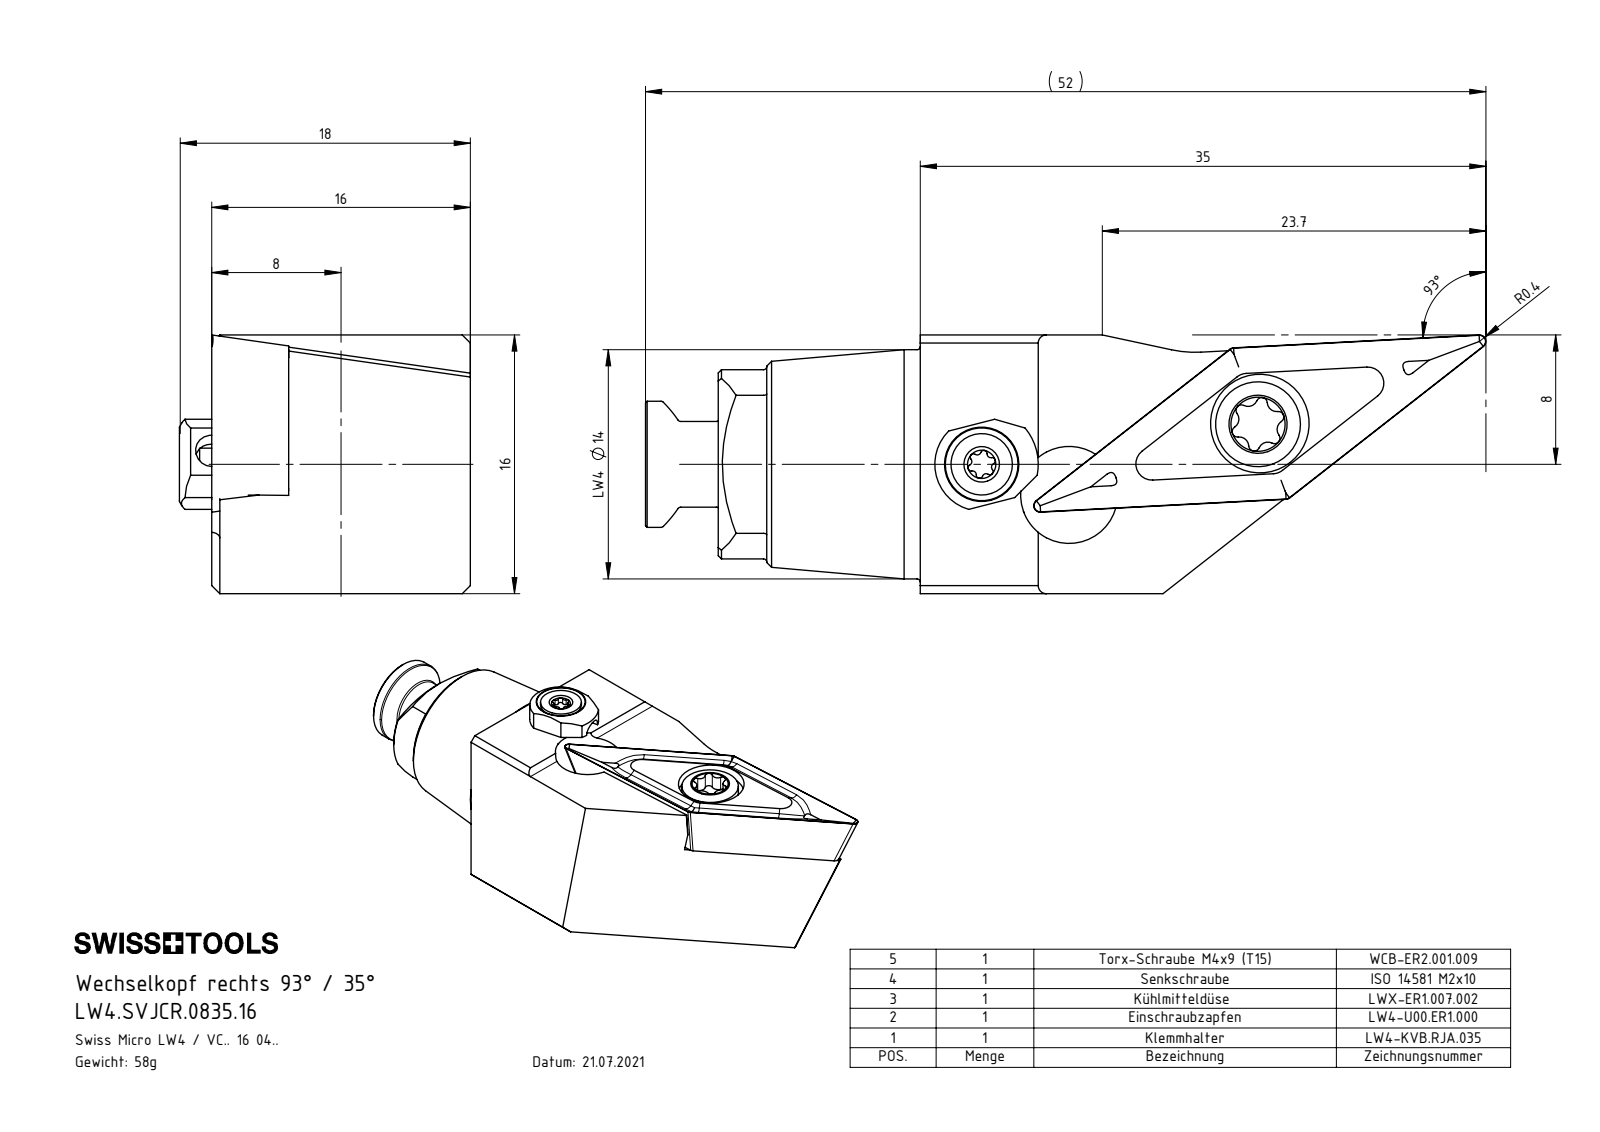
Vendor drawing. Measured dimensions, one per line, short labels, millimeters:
name: ISO 14581 - M2x10; LW4-U00.ER1.000_B; LW4-KVB.RJA.035_A; LWX-ER1.007.002 (+3 more)
written by: SolidWorks 2022 (CONFIG_CONTROL_DESIGN)
unit: mm
bodies: 6 solids, 270 faces (70 planar, 83 cylindrical, 117 other)
size: 52 × 18 × 16
volume: 6 929 mm³; area: 4 302 mm²
holes: 2× ⌀2, 1× ⌀1.6, 1× ⌀2.5, 1× ⌀3, 1× ⌀3.3, 1× ⌀4.4, 1× ⌀5.5, 1× ⌀6, 1× ⌀6.1
bosses: 1× ⌀14.17, 1× ⌀7.7, 1× ⌀6, 1× ⌀5.3, 1× ⌀5.25, 1× ⌀5, 1× ⌀4, 1× ⌀3.8
rounds: 8× R0.2, 6× R0.24, 6× R0.34, 6× R0.59, 1× R0.5, 1× R1, 1× R2.9, 1× R3.5
face distances: 16, 11.24, 4.76, 15.5, 4.26, 0.5, 7.5, 2, 3, 12.5
hole spacings: 5.73, 12.48, 12.6, 17.28, 17.39
